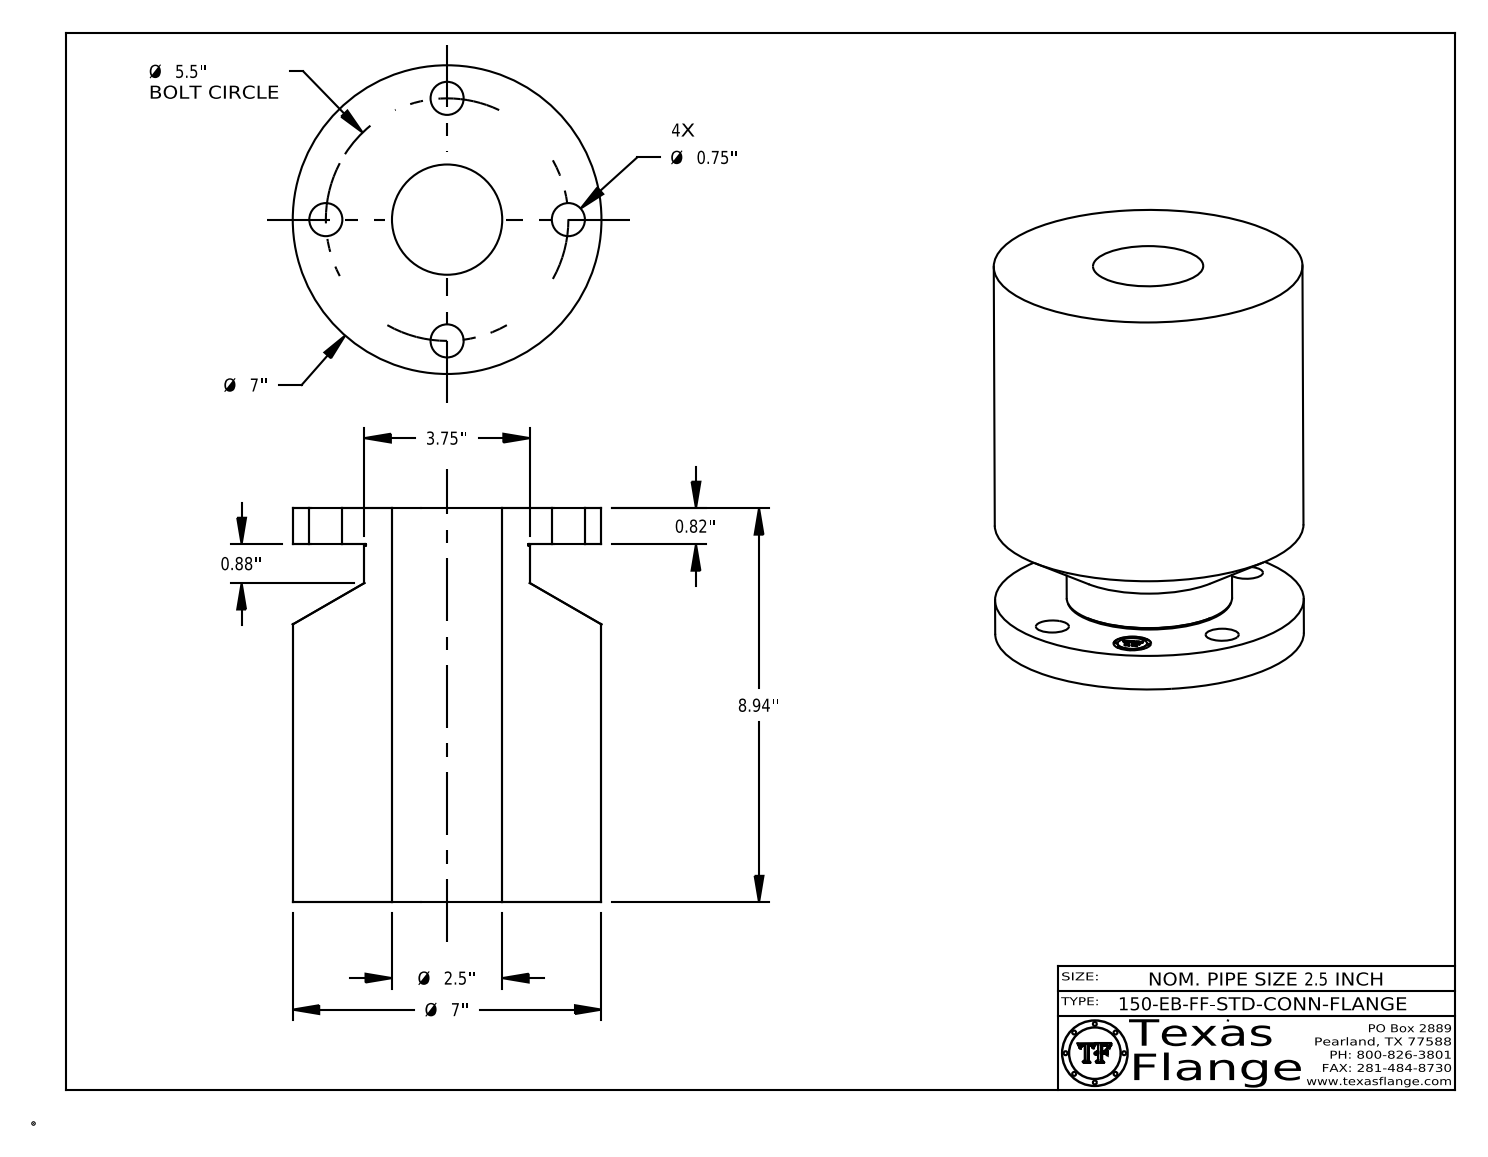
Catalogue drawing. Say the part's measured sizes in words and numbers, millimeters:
The part is named "2.5-150-EB-FF-STD-CONN-FLANGE". Its 3-D file was written by "CATIA V5 STEP AP214 (AUTOMOTIVE_DESIGN)". It is 1 solid with 410 faces: 368 planar, 36 cylindrical and 6 other. Overall it measures 227 by 177.8 by 177.8 millimeters. Its volume is 4 266 000 cubic millimeters and its surface area 237 500 square millimeters. Round holes: 4 of diameter 19.1, 1 of diameter 21.6, 1 of diameter 63.5. Round bosses or shafts: 8 of diameter 1.3, 1 of diameter 177.8, 1 of diameter 95.3, 1 of diameter 17. The main face-to-face distances are 227, 20.8, 206.2, 20.7, 206.4, 6.5, 6.3, 0.4, 1.2, 4.2. The hole center spacings are 69.9, 98.8, 53.5, 129.1, 139.7.
